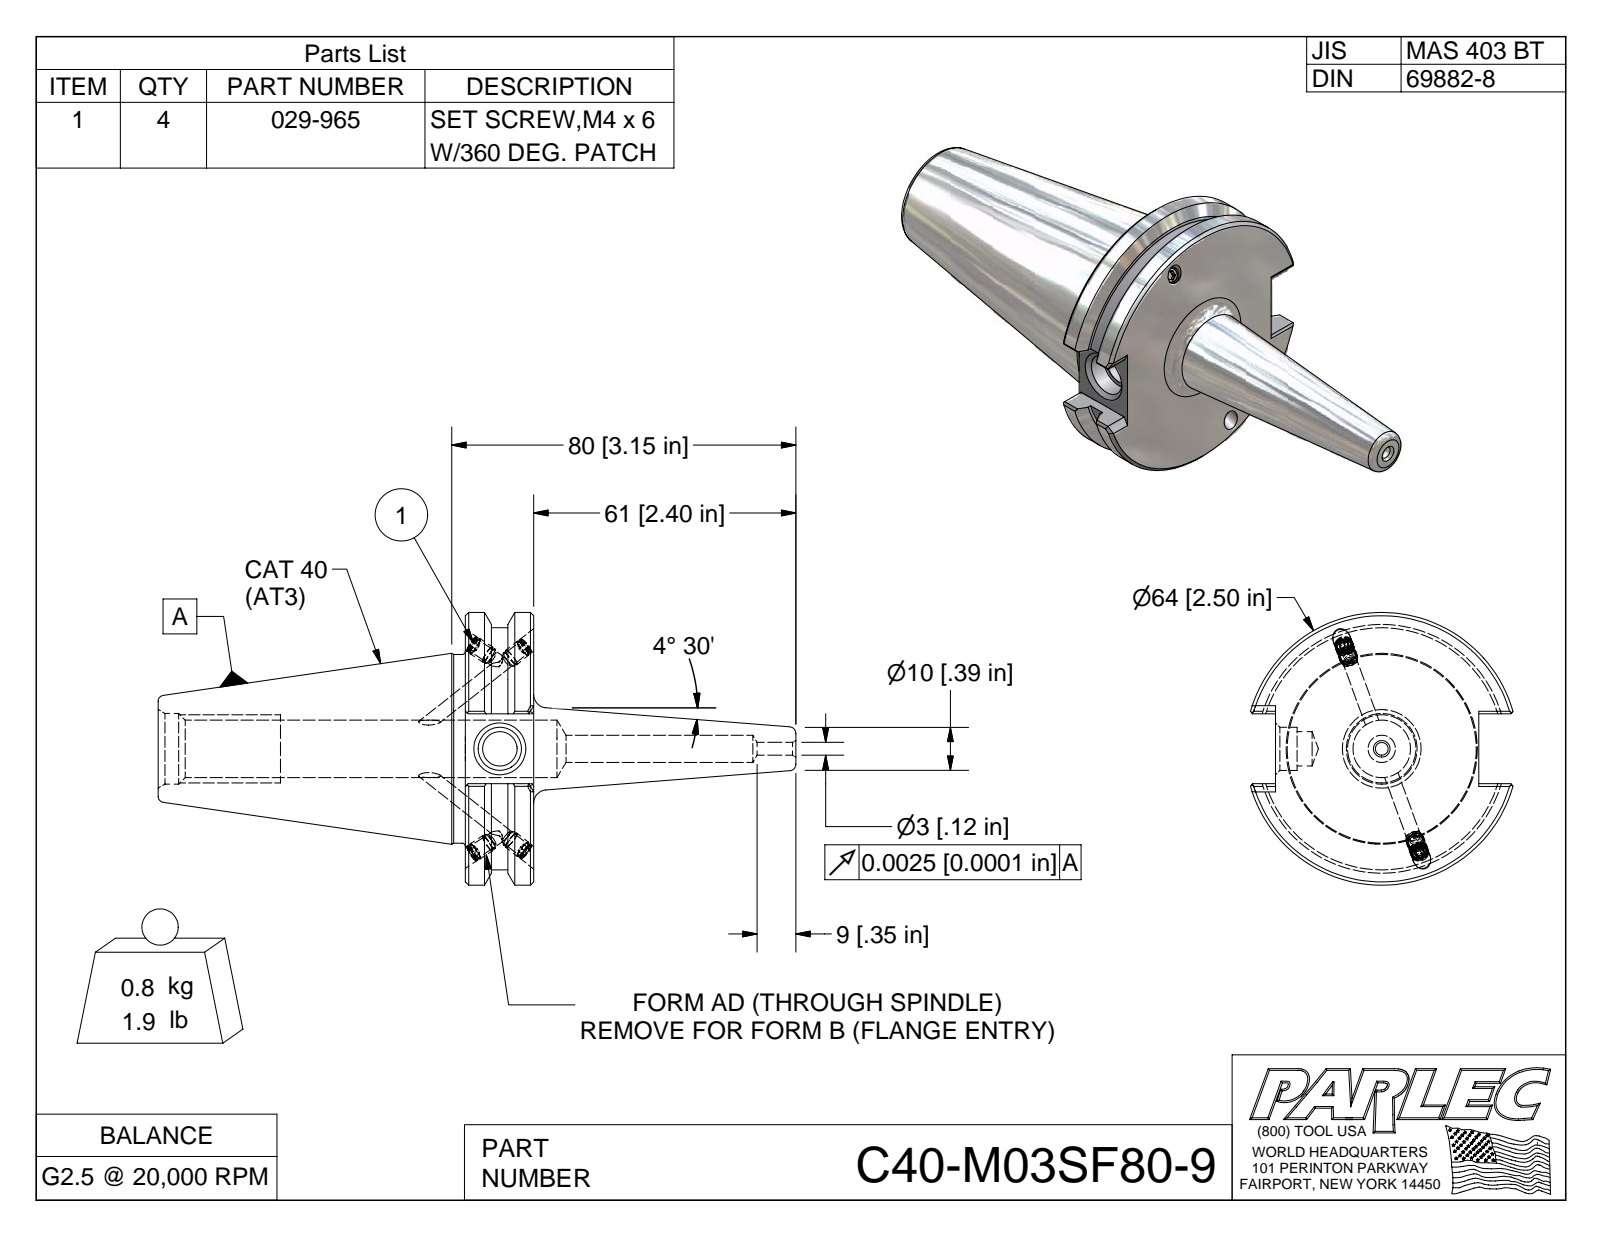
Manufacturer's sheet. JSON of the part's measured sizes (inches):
{"part_name": "C40-M03SF80-9; C40BC-M03SF80-9-1; 029-965", "step_written_by": "Autodesk Inventor 2009 (AUTOMOTIVE_DESIGN)", "units": "inches", "bodies": {"solids": 5, "faces": 148, "planar": 75, "cylindrical": 28, "other": 45}, "overall_size": [5.837, 2.5, 2.403], "volume_in3": 6.618, "surface_area_in2": 39.38, "round_holes": [[0.13, 4], [0.161, 4], [0.118, 1]], "round_bosses_or_shafts": [[0.165, 4], [0.157, 4], [2.5, 1], [2.219, 1], [1.73, 1]], "face_to_face_distances": [0.625, 0.64, 1.86, 2.812, 3.437, 3.201, 0.389, 0.236, 3.05, 0.238]}
